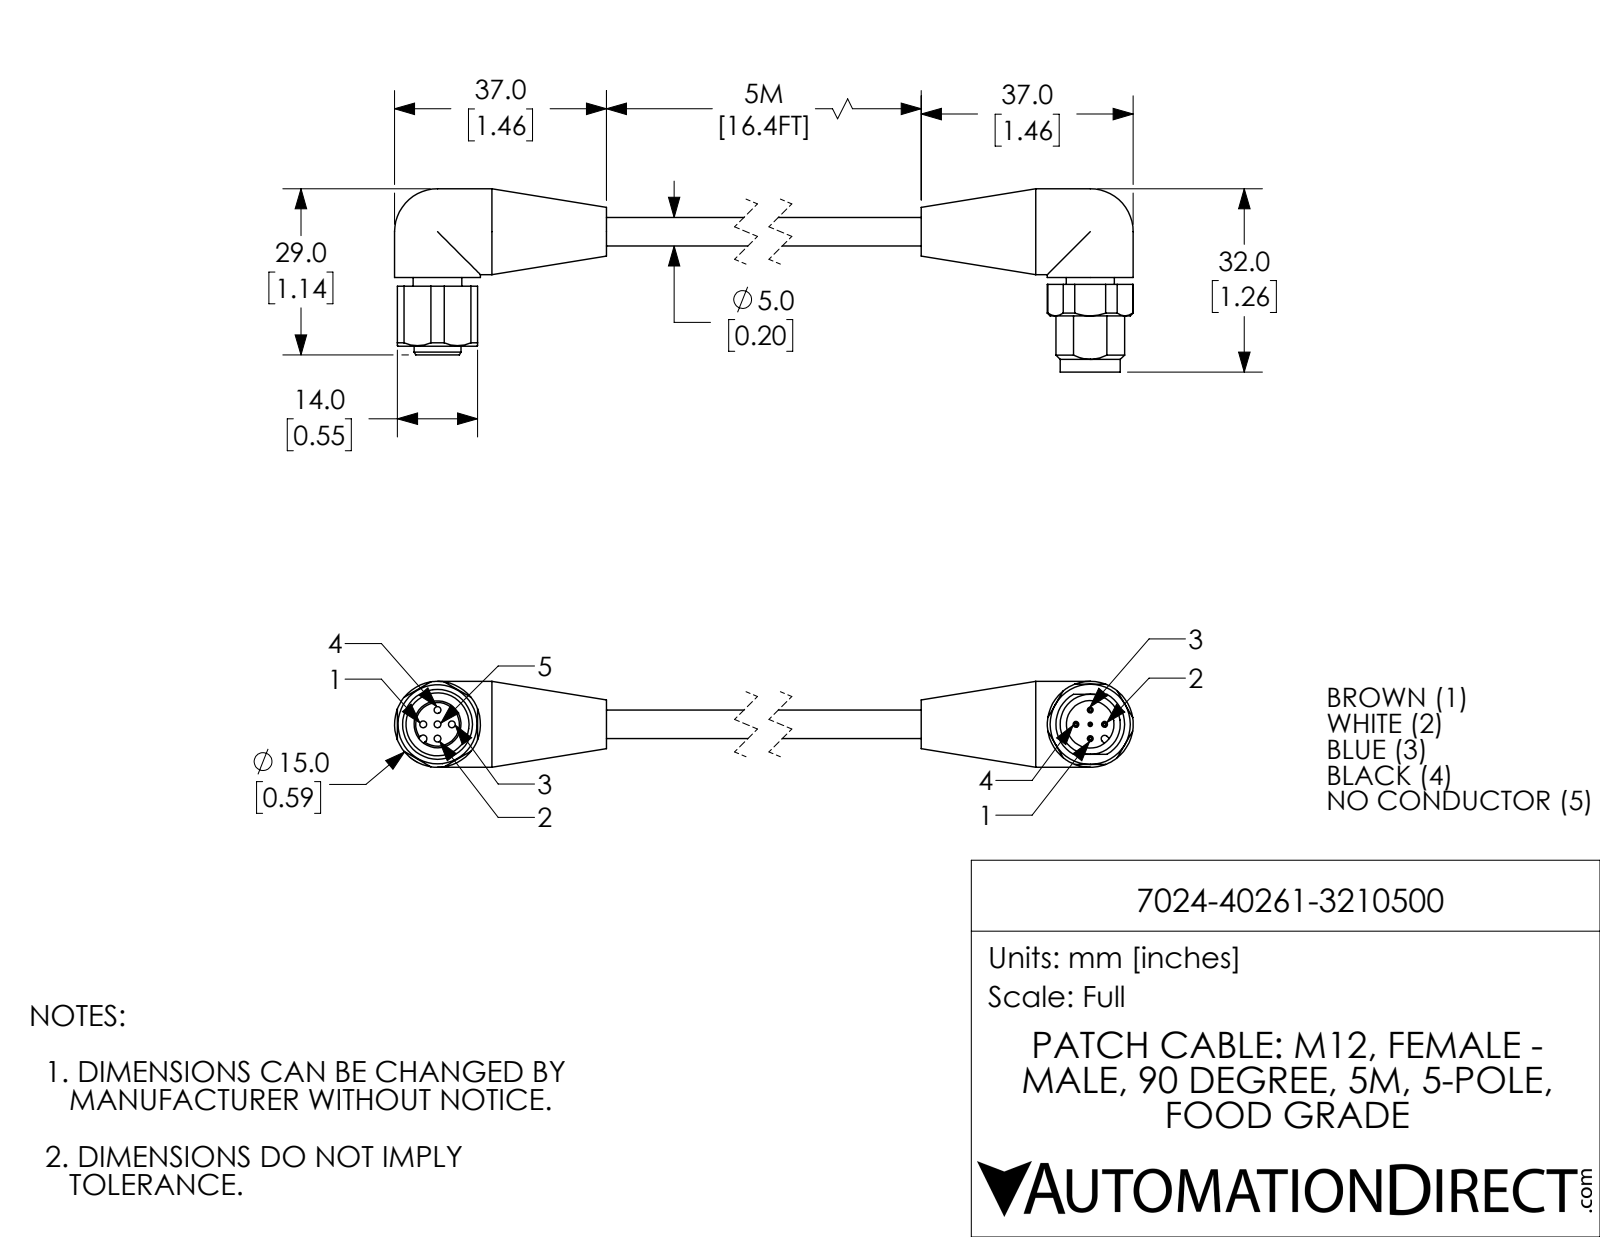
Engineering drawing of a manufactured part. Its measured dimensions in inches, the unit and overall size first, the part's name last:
Units: inches
Overall size (bounding box): 5.776 × 1.26 × 0.591
Round holes (diameter × count): ⌀0.047 ×5, ⌀0.327 ×1, ⌀0.433 ×1
Round bosses / shafts (diameter × count): ⌀0.039 ×4, ⌀0.591 ×3, ⌀0.413 ×1, ⌀0.335 ×1, ⌀0.331 ×1, ⌀0.323 ×1, ⌀0.197 ×1
Partial cylindrical surfaces — rounded edges, fillets, slot ends (radius × count): R0.024 ×1, R0.026 ×1, R0.236 ×1
Main face-to-face distances: 0.551, 0.059, 0.047, 0.472, 0.413, 0.177, 0.118, 0.069, 0.482, 0.217
Hole centre spacings: 0.098, 0.139, 0.197, 5.186, 5.087, 5.185, 5.283
Volume: 0.892 in³ · Surface area: 10.83 in²
Bodies: 2 solids, 135 faces (43 planar, 61 cylindrical, 31 other)
Part name (STEP PRODUCT): 7024-40261-3210500_MALE; 7024-40261-3210500; 7024-40261-3210500_FEMALE
STEP written by: SolidWorks 2018 (AUTOMOTIVE_DESIGN)
